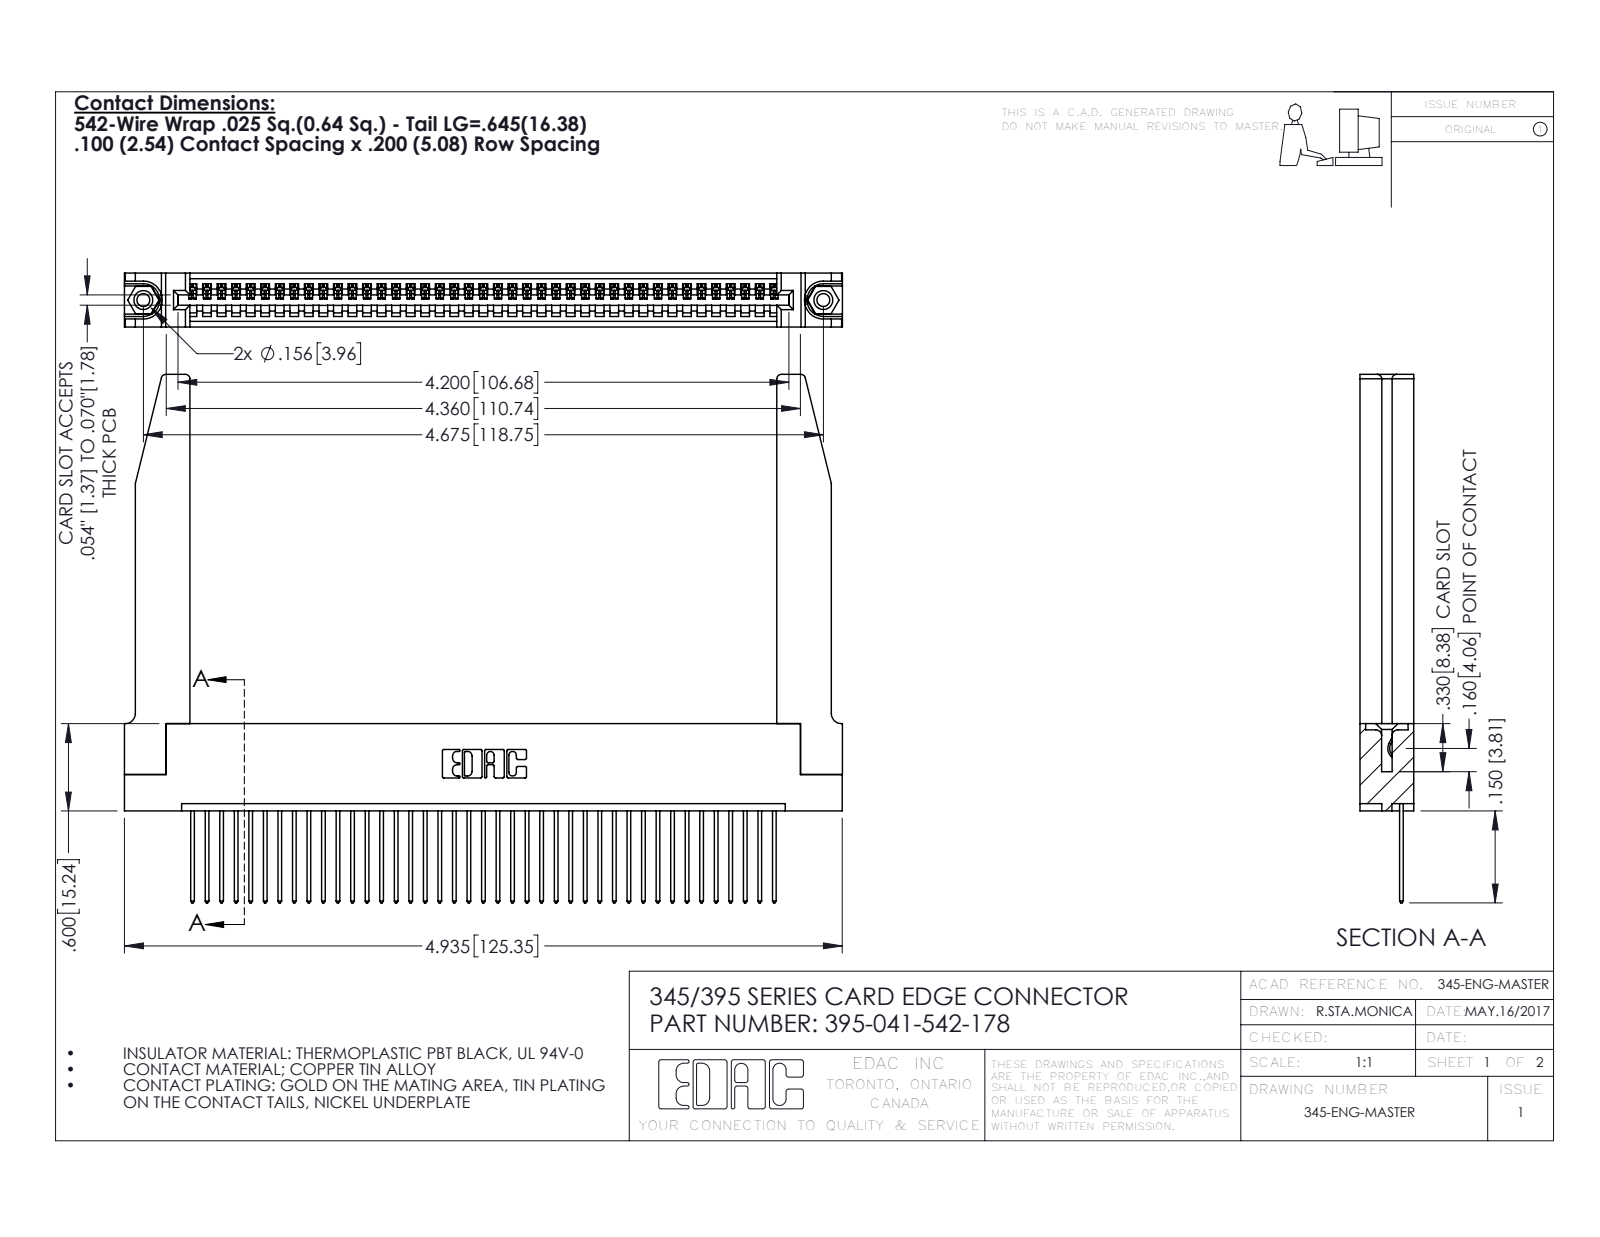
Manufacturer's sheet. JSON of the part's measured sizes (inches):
{"part_name": "345-220-078_345-220-078; 345 Part_Flush Mounting Lugs - 0.156 Dia-TH; 345-250-001_345-250-001-102; 345-292-001_345-293-142 (+1 more)", "step_written_by": "SolidWorks 2016 (CONFIG_CONTROL_DESIGN)", "units": "inches", "bodies": {"solids": 46, "faces": 2738, "planar": 1862, "cylindrical": 824, "other": 52}, "overall_size": [4.936, 3.632, 0.37], "volume_in3": 1.206, "surface_area_in2": 36.18, "round_holes": [[0.089, 2], [0.125, 2], [0.156, 2], [0.064, 1]], "round_bosses_or_shafts": [[0.155, 2]], "partial_cylinders_radius": [[0.006, 82], [0.01, 82], [0.01, 22], [0.03, 8], [0.007, 6], [0.031, 6], [0.026, 3], [0.031, 2]], "face_to_face_distances": [0.37, 0.072, 0.298, 0.098, 0.272, 0.025, 0.2, 0.225, 0.148, 0.15], "hole_center_spacings": [0.27, 4.439, 4.675]}
